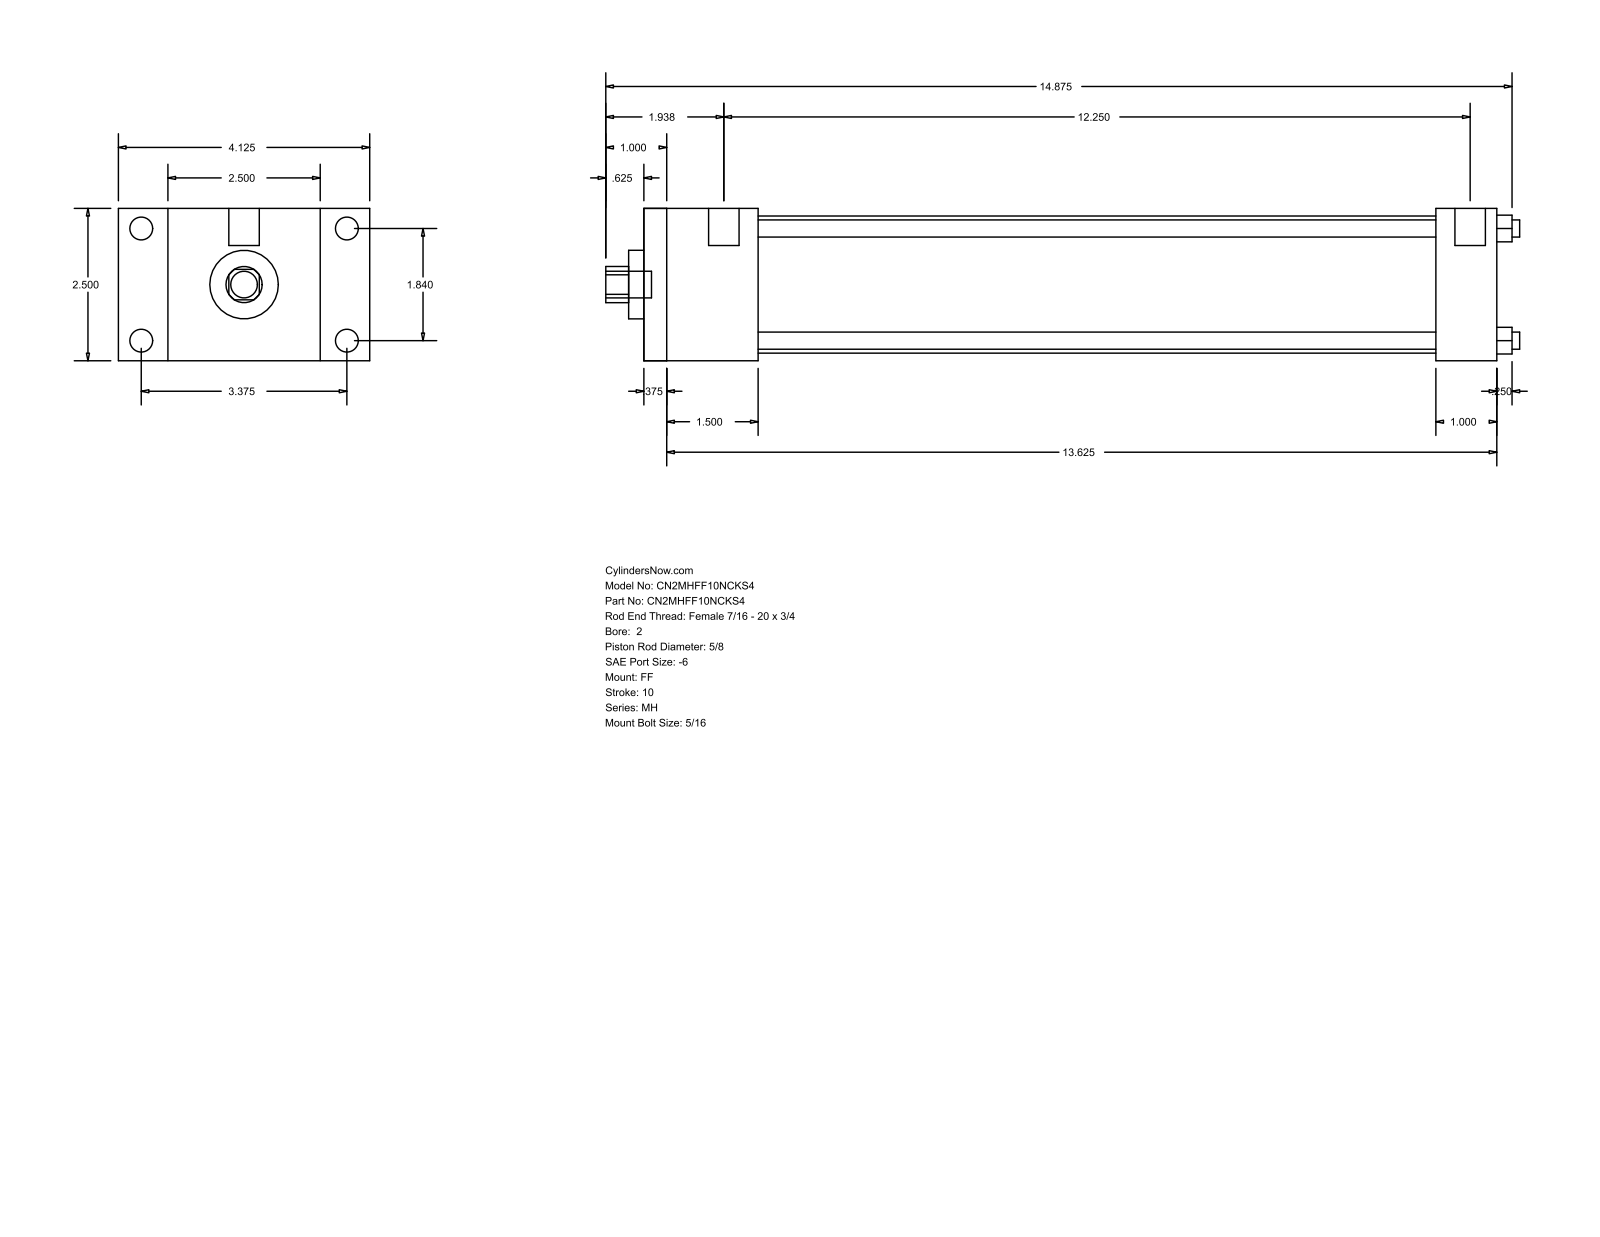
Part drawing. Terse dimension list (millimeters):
name: MH_FF__0200_0.625
written by: GSSL Pune (CONFIG_CONTROL_DESIGN)
unit: mm
bodies: 0 solids, 92 faces (64 planar, 28 cylindrical, 0 other)
size: 381 × 104.78 × 63.5
holes: 4× ⌀7.14, 1× ⌀15.88, 1× ⌀28.57, 1× ⌀57.15
bosses: 4× ⌀9.53, 4× ⌀5.56, 2× ⌀12.7, 1× ⌀11.11
rounds: 1× R7.54
face distances: 63.5, 355.6, 9.52, 346.08, 38.1, 47.62, 330.19, 320.67, 282.57, 307.98
hole spacings: 33.05, 46.74, 66.1
